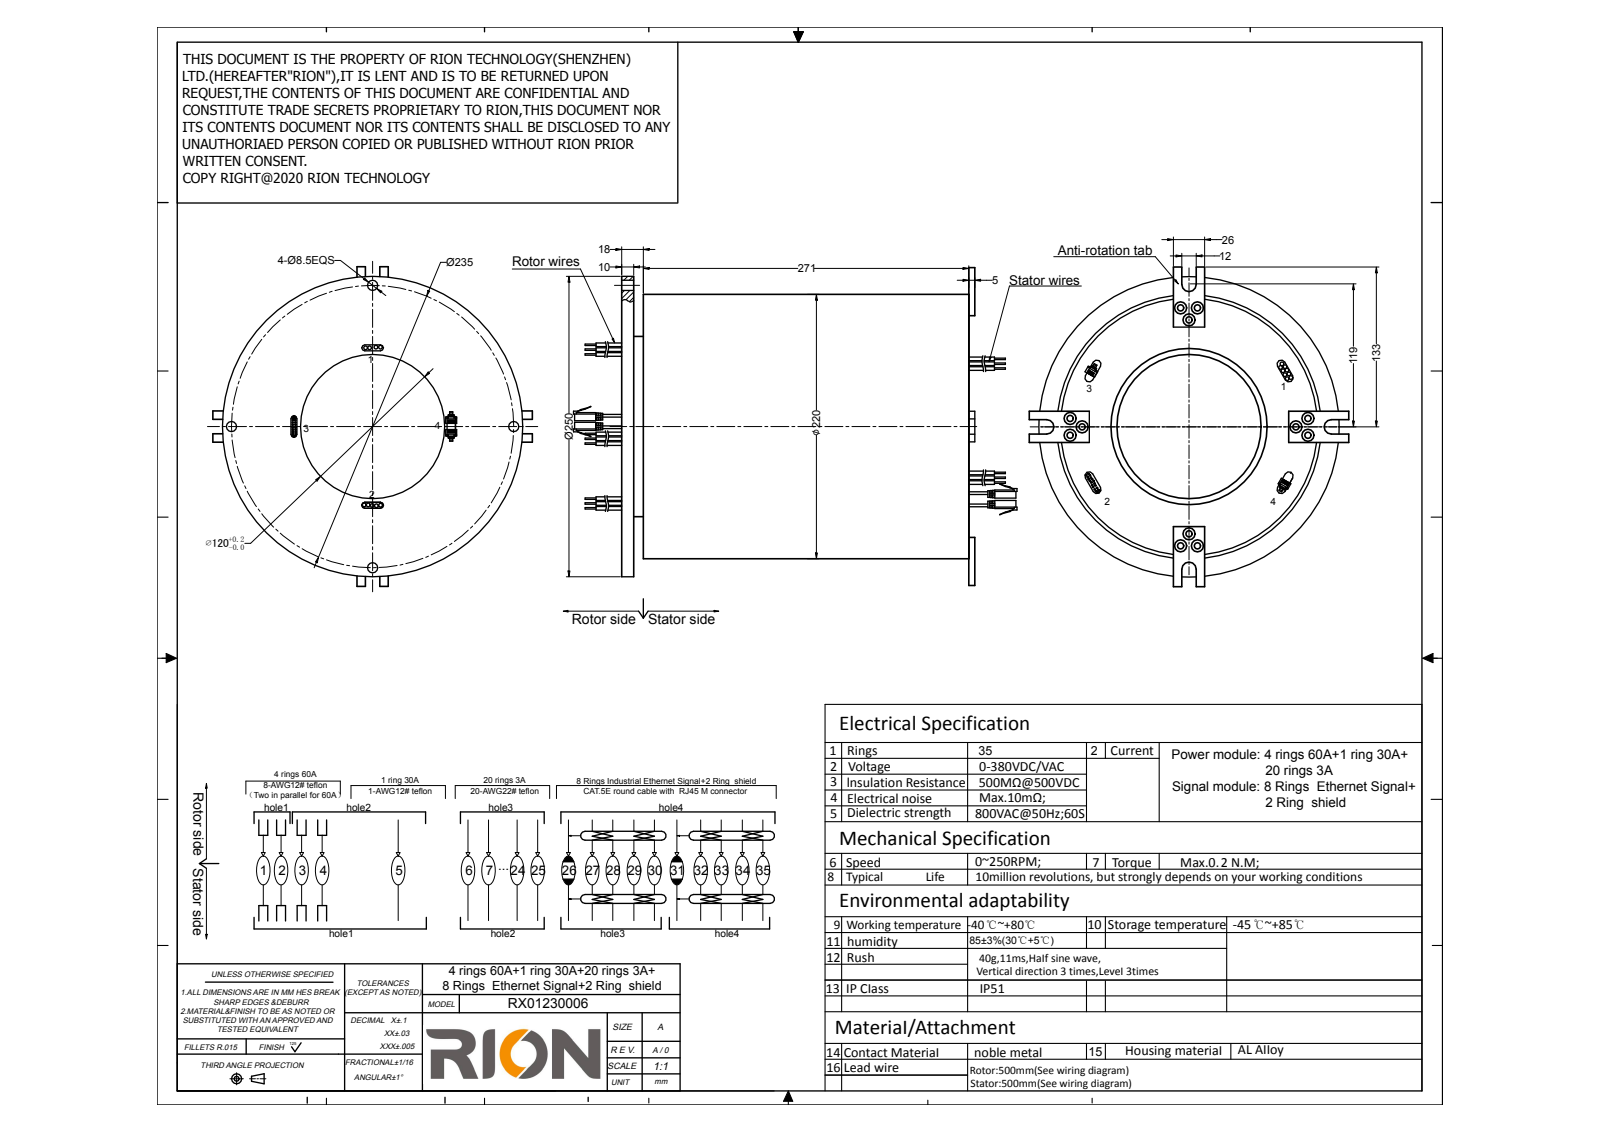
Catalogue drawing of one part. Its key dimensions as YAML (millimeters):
step_written_by: "SolidWorks 2014 (CONFIG_CONTROL_DESIGN)"
units: millimeters
bodies: {solids: 1, faces: 369, planar: 144, cylindrical: 201, other: 24}
overall_size: [329, 266.01, 266.01]
volume: 7688000
surface_area: 443283
round_holes:
  - {diameter: 5.2, count: 12}
  - {diameter: 8.5, count: 4}
  - {diameter: 120, count: 1}
  - {diameter: 130.4, count: 1}
  - {diameter: 214.4, count: 1}
round_bosses_or_shafts:
  - {diameter: 1.3, count: 40}
  - {diameter: 3.2, count: 18}
  - {diameter: 6.5, count: 4}
  - {diameter: 250, count: 1}
  - {diameter: 220, count: 1}
  - {diameter: 214, count: 1}
  - {diameter: 150, count: 1}
  - {diameter: 130, count: 1}
partial_cylinders:
  - {radius: 3.5, count: 8}
  - {radius: 2.5, count: 6}
  - {radius: 6, count: 4}
face_to_face_distances: [10, 289, 279, 8, 18, 271, 5, 294, 284, 276]
hole_center_spacings: [12.21, 19.78, 99.25, 128.55, 137.9, 140.36, 147.4, 148.36]
